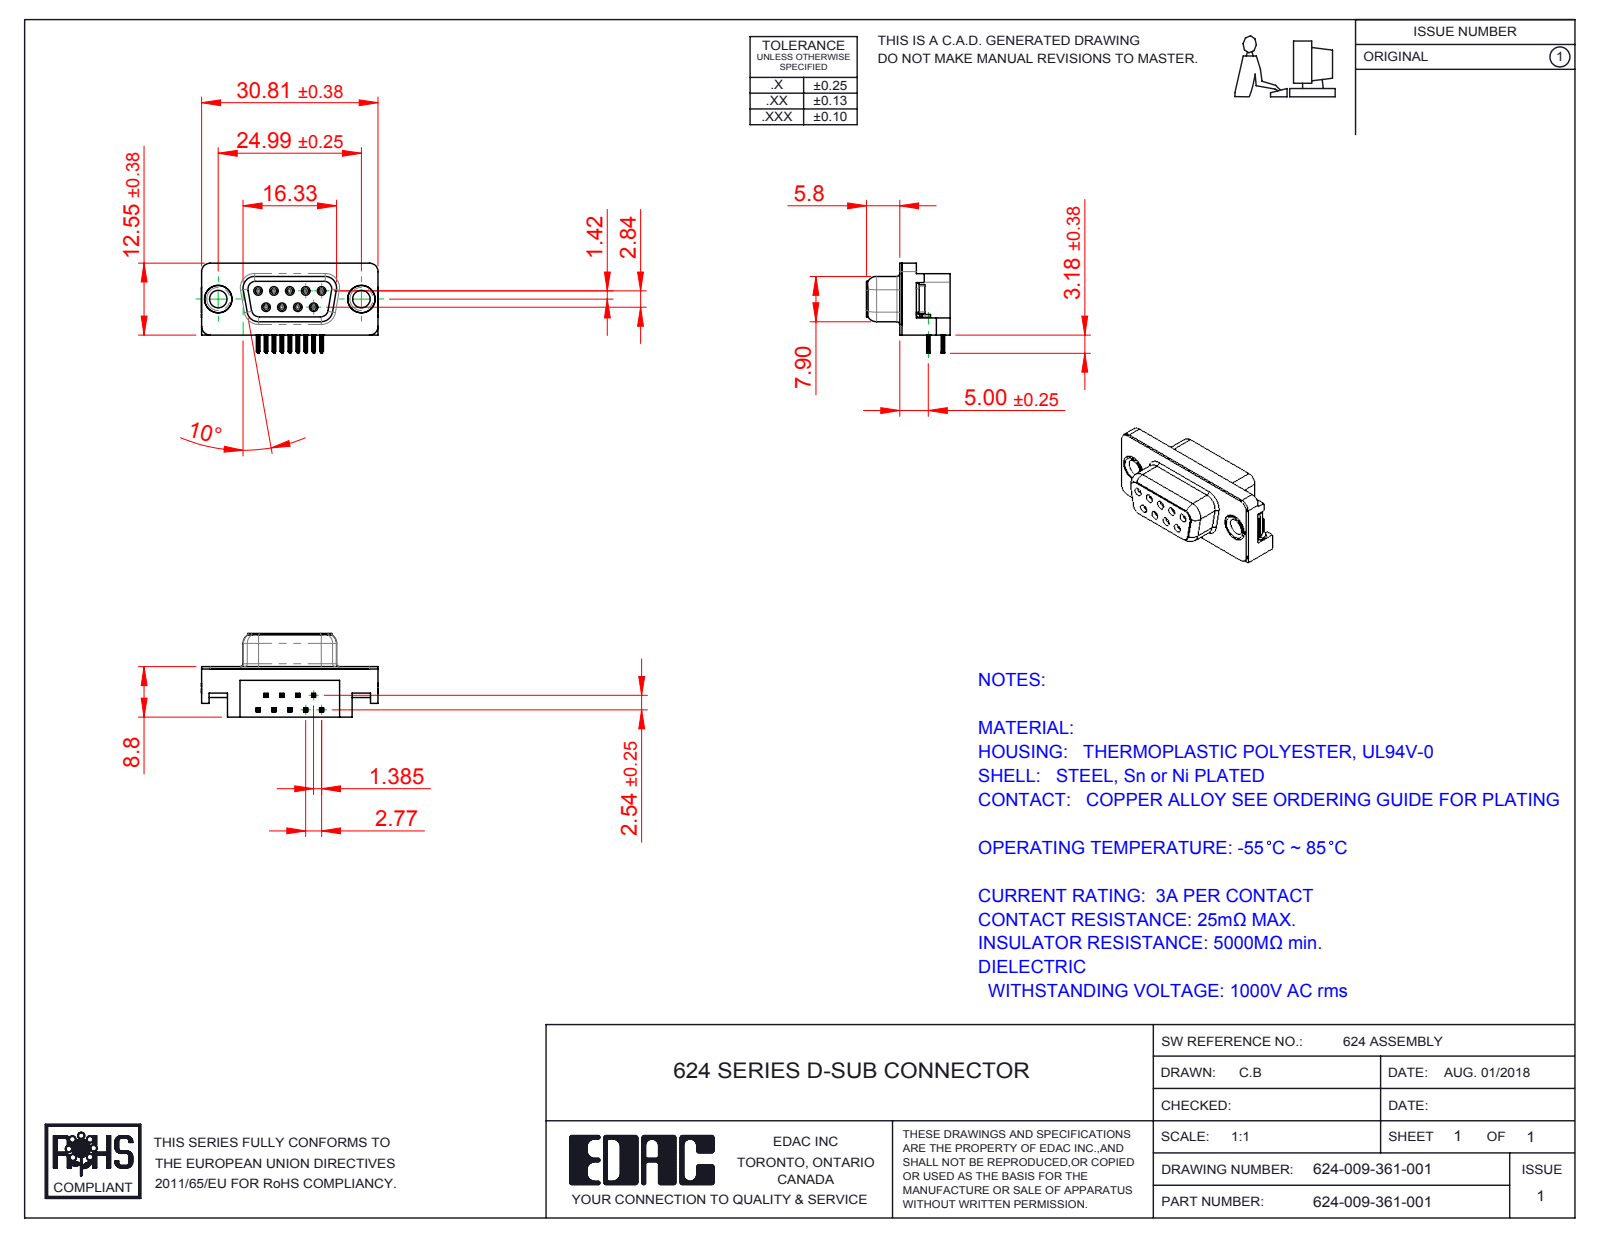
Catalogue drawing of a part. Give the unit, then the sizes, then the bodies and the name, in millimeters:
Units: millimetres
Overall size (bounding box): 30.89 × 15.73 × 14.6
Round holes (diameter × count): ⌀0.8 ×9, ⌀0.9 ×9, ⌀3.05 ×2, ⌀4 ×2, ⌀4.8 ×2, ⌀5 ×2
Round bosses / shafts (diameter × count): ⌀1.2 ×9, ⌀4.9 ×2, ⌀4.75 ×2, ⌀3.85 ×2
Partial cylindrical surfaces — rounded edges, fillets, slot ends (radius × count): R0.1 ×72, R0.15 ×36, R0.35 ×18, R1 ×18, R0.34 ×9, R0.25 ×8, R1.35 ×8, R1.5 ×7
Main face-to-face distances: 0.4, 8.4, 8.8, 2.9, 2.5, 6.2, 5.9, 0.35, 10.69, 10.34
Hole centre spacings: 3.16, 2.77, 5.54, 5.03, 5.04, 8.31, 7.48, 7.49
Volume: 2 925 mm³ · Surface area: 4 311 mm²
Bodies: 15 solids, 1480 faces (642 planar, 388 cylindrical, 450 other)
Part name (STEP PRODUCT): 624-009-361-001; 624 Thru Hole Rivet; 624 Non Board Mount; 624 Contact Top (+3 more)
STEP written by: SolidWorks 2016 (CONFIG_CONTROL_DESIGN)
